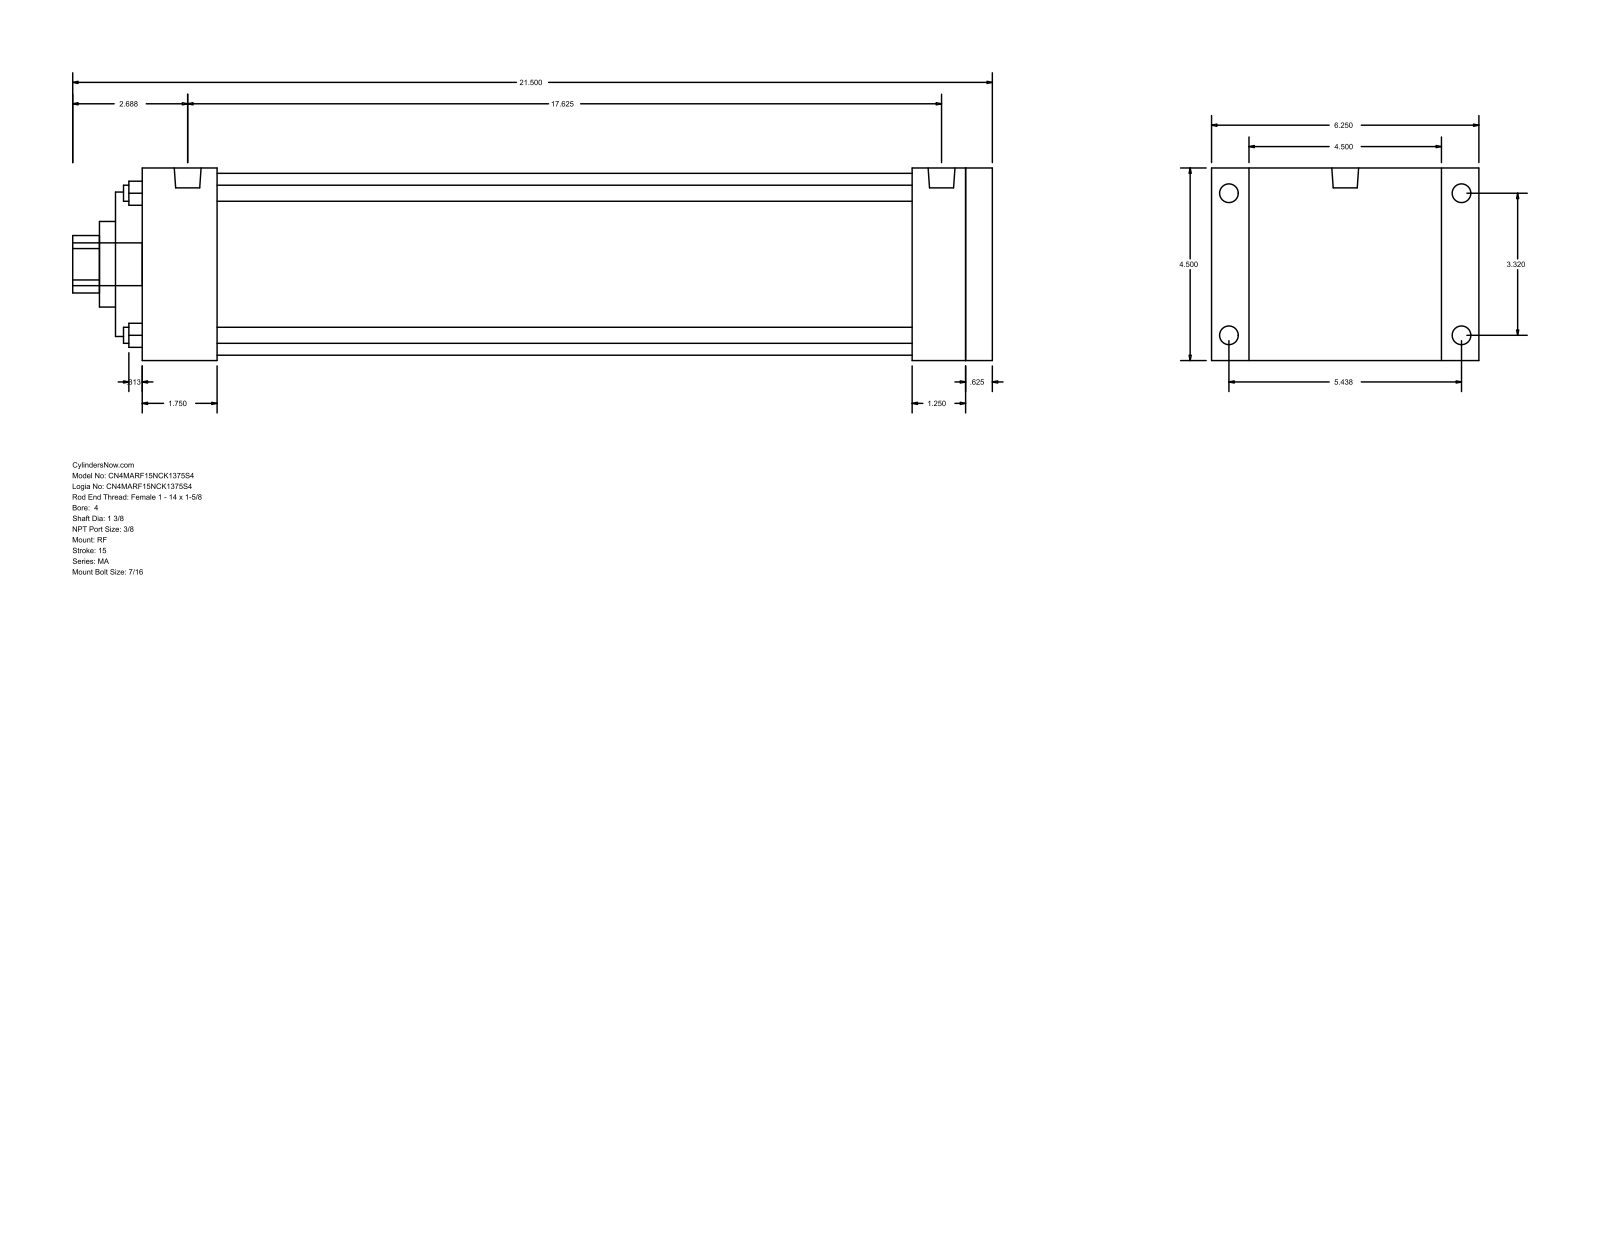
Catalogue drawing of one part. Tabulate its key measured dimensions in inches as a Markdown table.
| quantity | value |
| --- | --- |
| part name | MA_RF__0400_1.375 |
| STEP written by | GSSL Pune (CONFIG_CONTROL_DESIGN) |
| units | inches |
| bodies | 0 solids, 94 faces (65 planar, 29 cylindrical, 0 other) |
| overall size | 21.5 × 6.25 × 4.5 |
| round holes (diameter × count) | 0.375 × 4, 1.375 × 1, 2 × 1, 3.375 × 1, 4.25 × 1 |
| round bosses / shafts (diameter × count) | 0.437 × 8, 0.627 × 2, 1 × 1 |
| partial cylindrical surfaces (radius × count) | 0.672 × 1 |
| main face-to-face distances | 4.5, 19.875, 0.625, 19.25, 20.5, 0.875, 5.375, 18.625, 18, 1.25 |
| hole center spacings | 2.347, 3.32, 4.695 |
